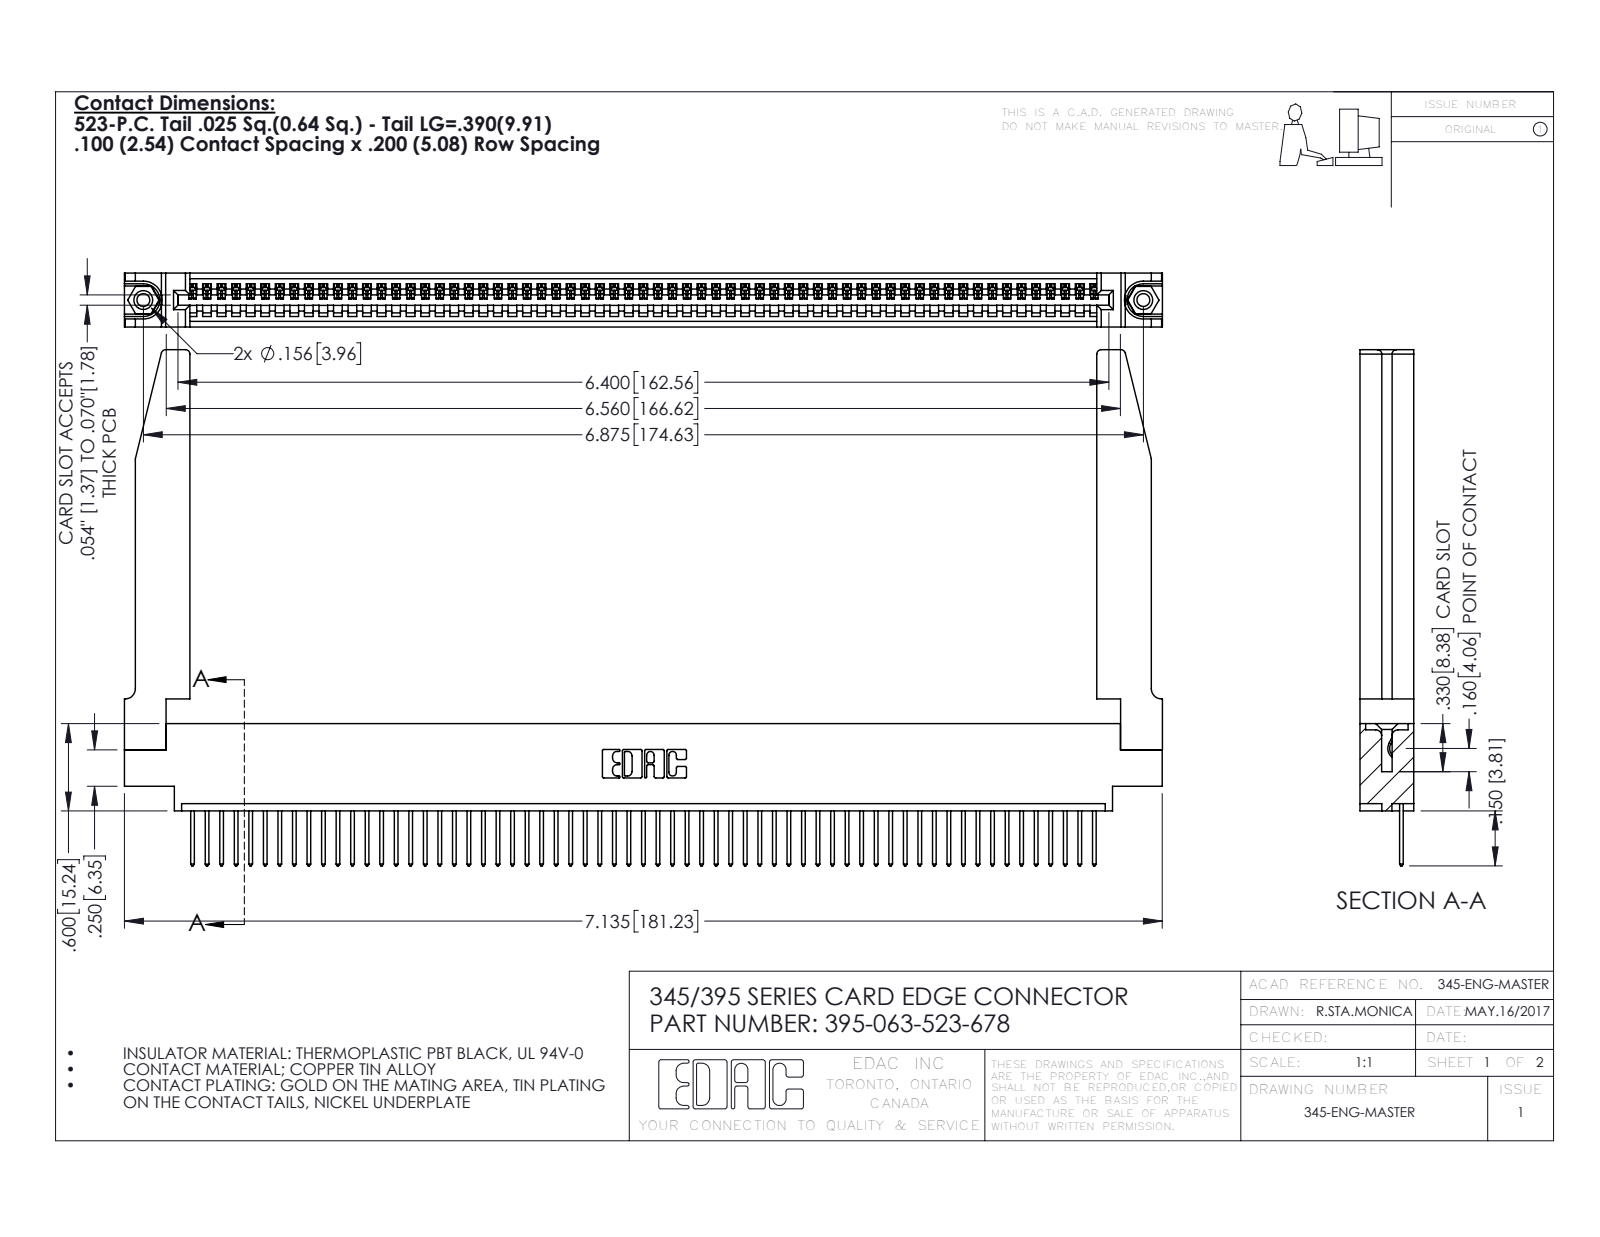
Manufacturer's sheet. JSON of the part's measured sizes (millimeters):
{"part_name": "345-220-078_345-220-078; 345 Part_0.170 Offset - 0.156 Dia-TH; 395-063-523-678; 345-250-001_345-250-001-102 (+1 more)", "step_written_by": "SolidWorks 2016 (CONFIG_CONTROL_DESIGN)", "units": "millimeters", "bodies": {"solids": 68, "faces": 4018, "planar": 2746, "cylindrical": 1220, "other": 52}, "overall_size": [181.3, 90.1, 9.4], "volume_mm3": 25020, "surface_area_mm2": 30250, "round_holes": [[2.3, 2], [3.2, 2], [4, 2], [1.6, 1]], "round_bosses_or_shafts": [[3.9, 2]], "partial_cylinders_radius": [[0.2, 126], [0.3, 126], [0.3, 22], [0.8, 8], [0.2, 6], [0.8, 6], [0.7, 3], [0.8, 2]], "face_to_face_distances": [1.8, 9.4, 7.6, 2.5, 6.9, 0.6, 5.1, 5.7, 3.8, 3.8], "hole_center_spacings": [6.9, 168.6, 174.6]}
